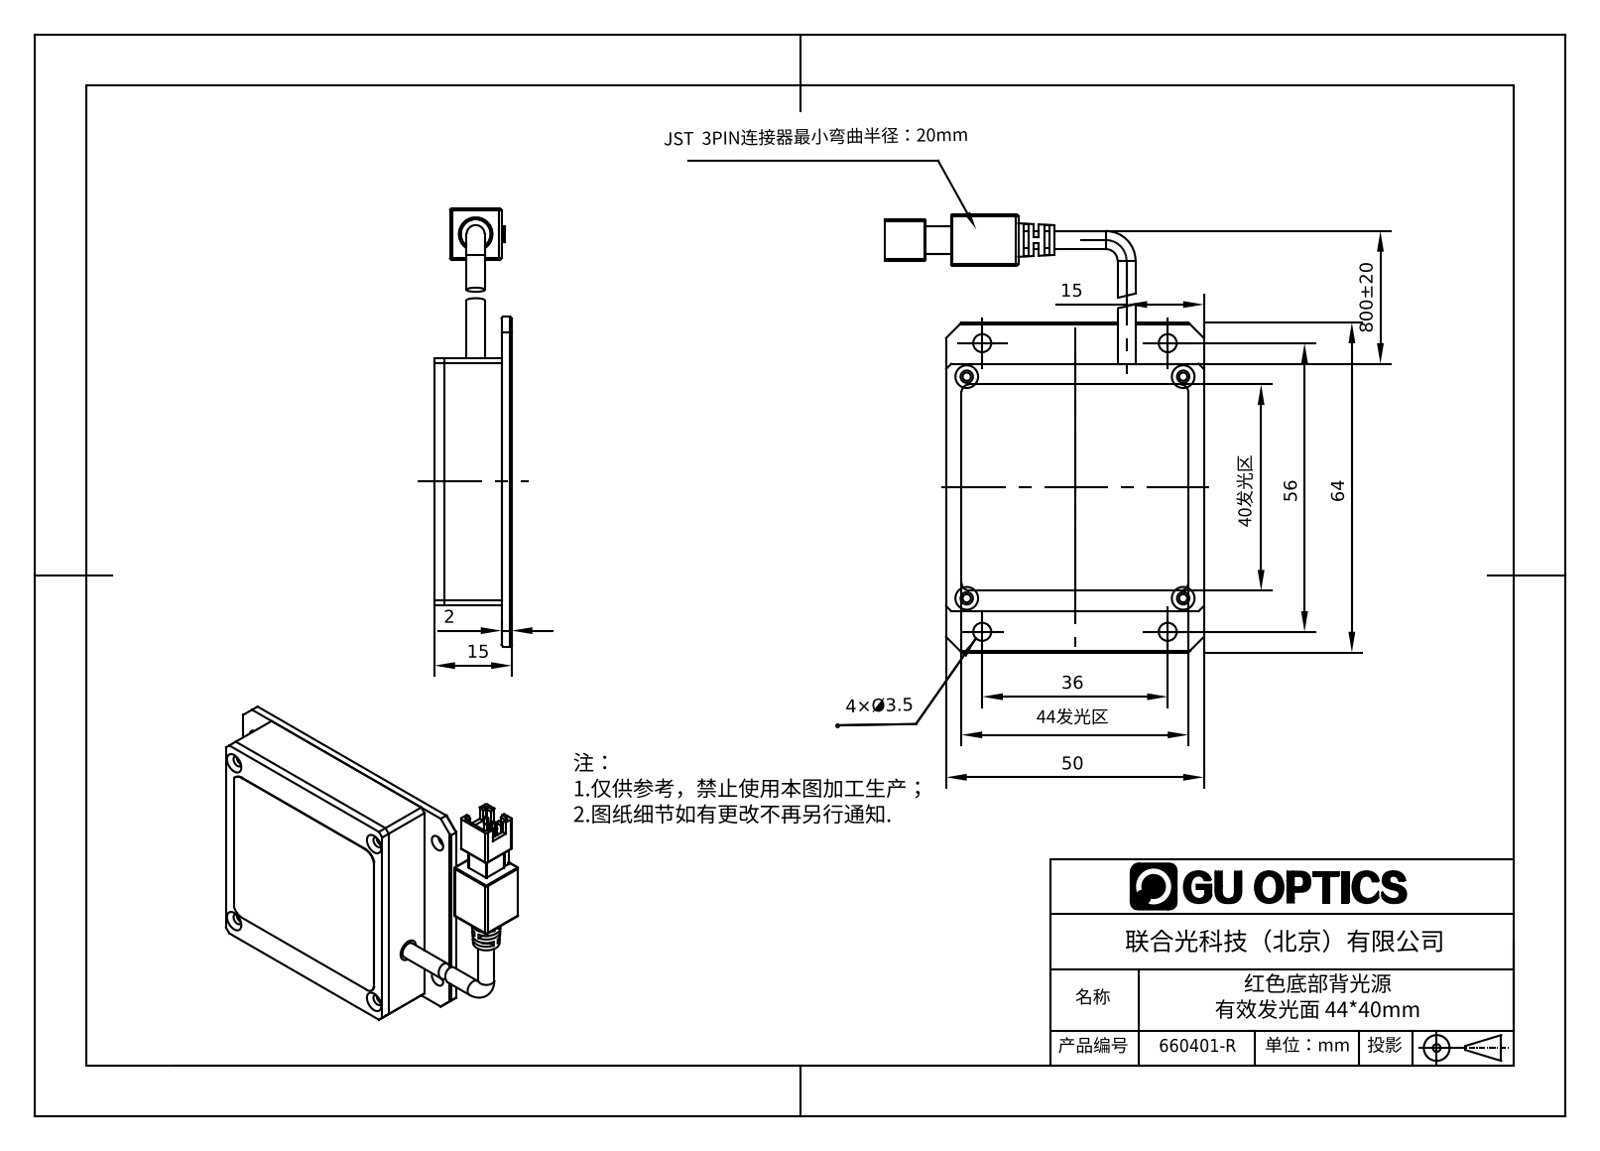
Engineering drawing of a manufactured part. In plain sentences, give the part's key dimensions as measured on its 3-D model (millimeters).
The part is named "660401-R". Its 3-D file was written by "SolidWorks 2016 (AUTOMOTIVE_DESIGN)". It is 6 solids with 476 faces: 239 planar, 118 cylindrical and 119 other. Overall it measures 85 by 62 by 15.1 millimeters. Its volume is 21 731 cubic millimeters and its surface area 23 523 square millimeters. Round holes: 8 of diameter 1.6, 8 of diameter 2.4, 4 of diameter 3.5. Round bosses or shafts: 2 of diameter 3.5. Partial cylindrical surfaces (rounded edges, fillets, slot ends): 15 of radius 0.1, 13 of radius 0.2, 12 of radius 0.4, 6 of radius 1.5, 4 of radius 1, 1 of radius 0.3, 1 of radius 0.68, 1 of radius 1.4. The main face-to-face distances are 2, 13, 11, 3, 1, 10, 2.1, 12.1, 15.1, 13.1. The hole center spacings are 1, 6.26, 7.16, 39.39, 39.54, 42, 42.01, 44.
